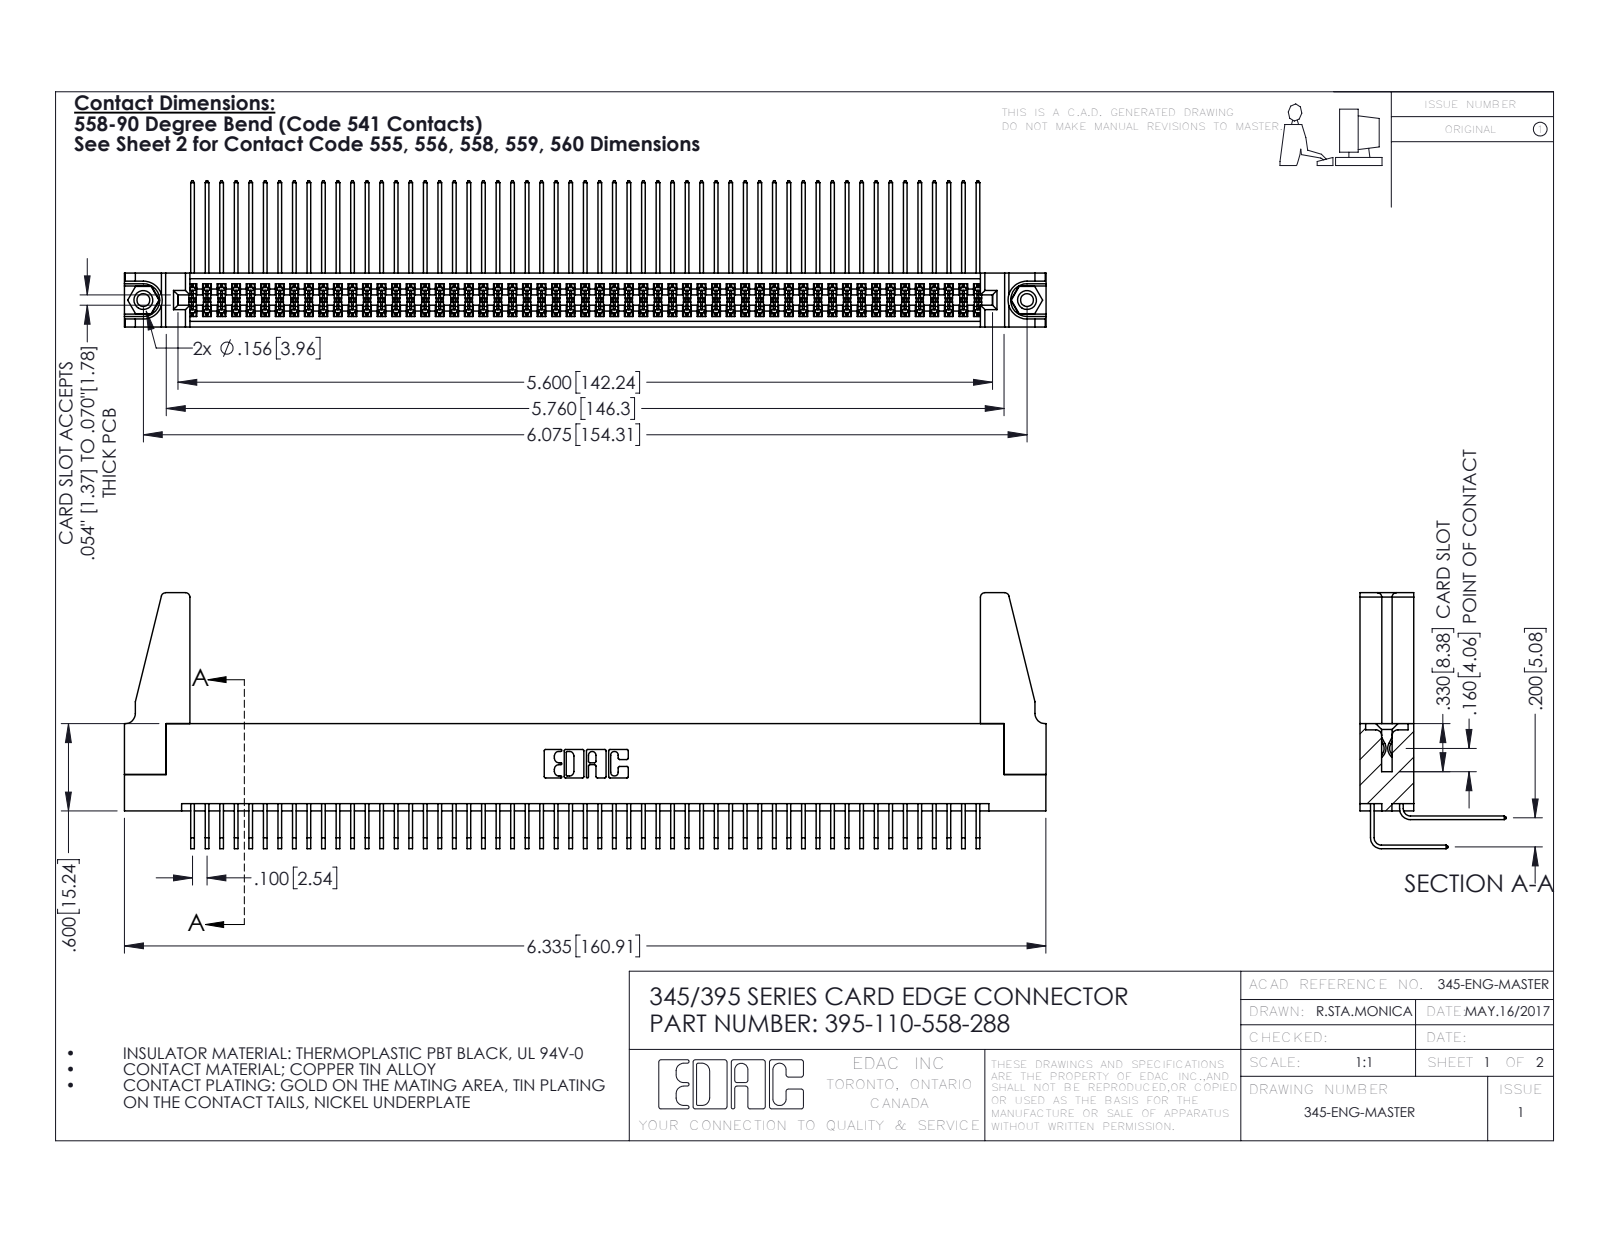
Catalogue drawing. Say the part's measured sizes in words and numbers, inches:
The part is named "395-110-558-288; 345-250-001_345-250-001-102; 345 Part_Flush Mounting Lugs - 0.156 Dia-TH; 345-220-078_345-220-088 (+2 more)". Its 3-D file was written by "SolidWorks 2016 (CONFIG_CONTROL_DESIGN)". It is 115 solids with 5970 faces: 4002 planar, 1952 cylindrical and 16 other. Overall it measures 6.336 by 1.759 by 1.005 inches. Its volume is 1.199 cubic inches and its surface area 47.4 square inches. Round holes: 2 of diameter 0.089, 2 of diameter 0.125, 2 of diameter 0.156, 1 of diameter 0.064. Round bosses or shafts: 2 of diameter 0.155. Partial cylindrical surfaces (rounded edges, fillets, slot ends): 165 of radius 0.006, 22 of radius 0.01, 8 of radius 0.03, 6 of radius 0.007, 6 of radius 0.031, 3 of radius 0.026, 2 of radius 0.014, 2 of radius 0.019. The main face-to-face distances are 0.072, 0.298, 0.2, 0.37, 0.098, 0.272, 0.025, 0.225, 0.025, 0.285. The hole center spacings are 0.27, 5.839, 6.075.
